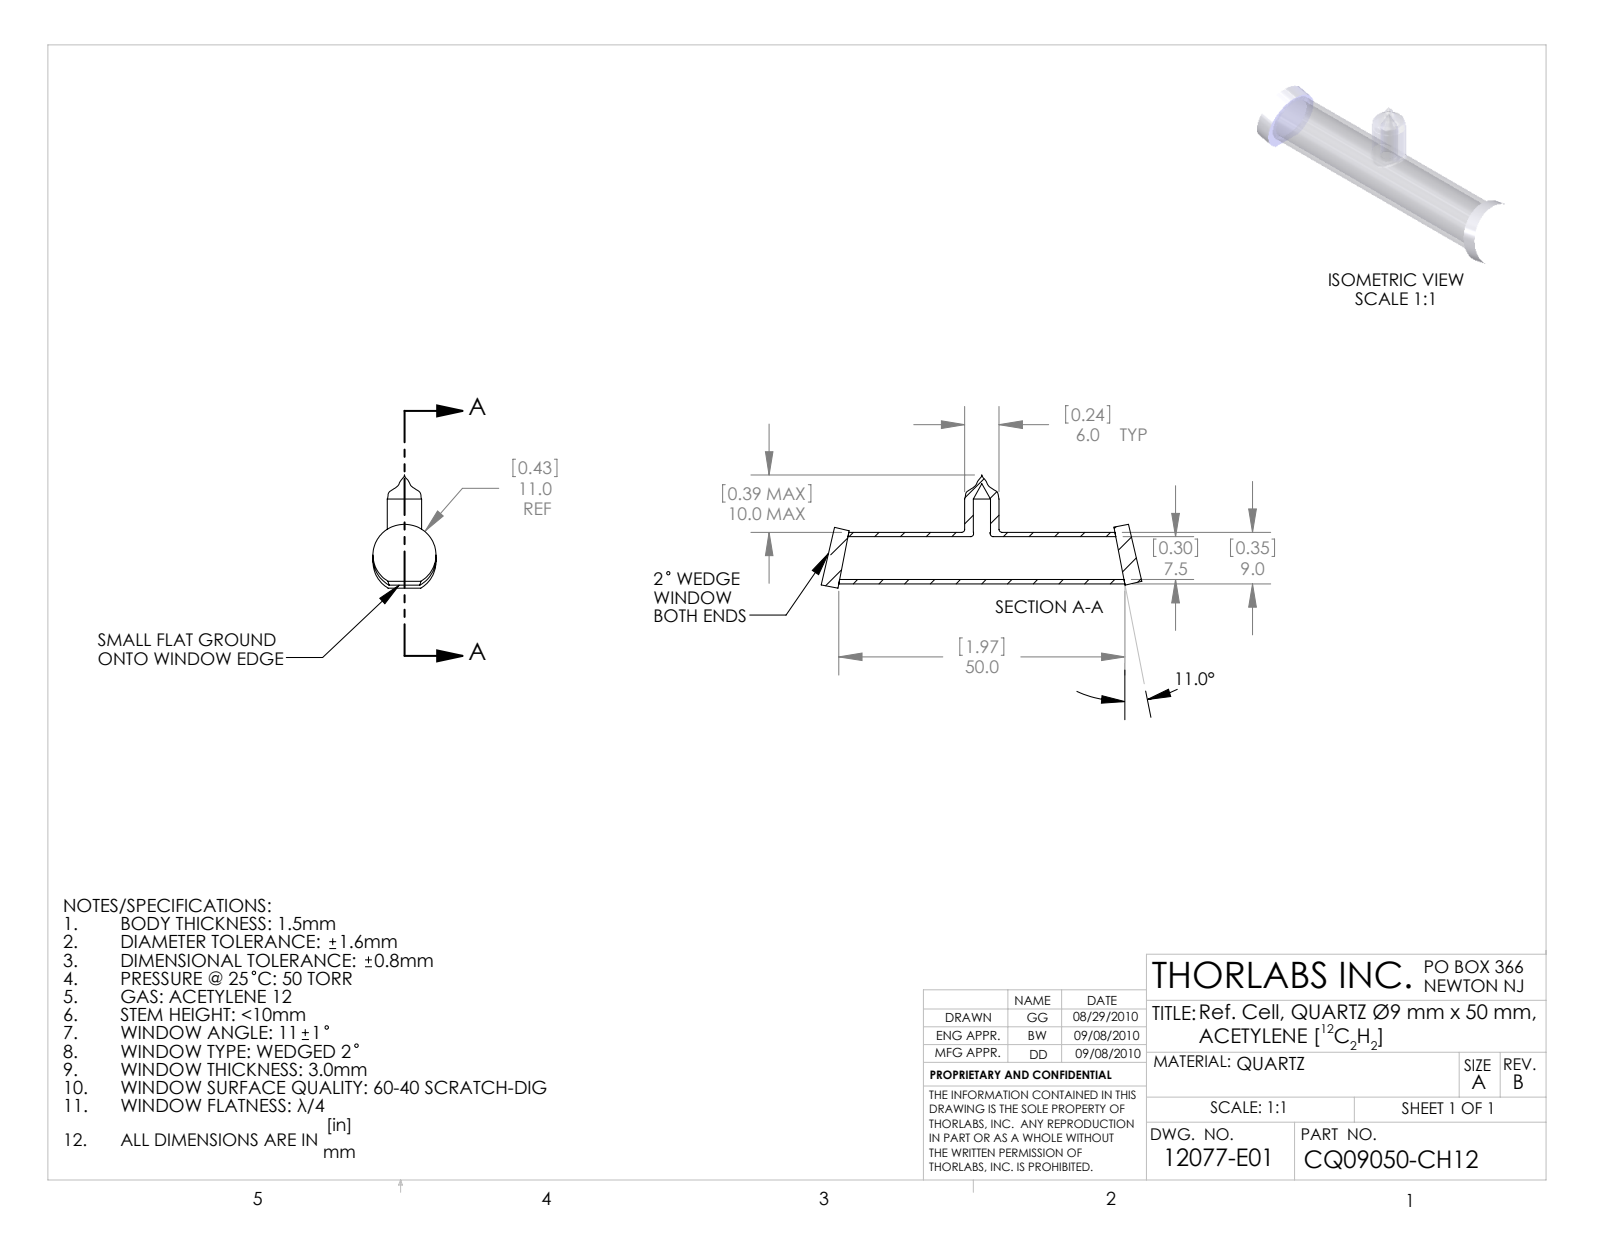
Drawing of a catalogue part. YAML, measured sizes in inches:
part_name: "12077-E0W"
step_written_by: "SolidWorks 2009 (AUTOMOTIVE_DESIGN)"
units: inches
bodies: {solids: 3, faces: 33, planar: 8, cylindrical: 17, other: 8}
overall_size: [2.203, 0.777, 0.433]
volume: 0.099
surface_area: 5.132
round_holes:
  - {diameter: 0.115, count: 1}
  - {diameter: 0.118, count: 1}
  - {diameter: 0.295, count: 1}
round_bosses_or_shafts:
  - {diameter: 0.433, count: 2}
  - {diameter: 0.354, count: 1}
  - {diameter: 0.236, count: 1}
